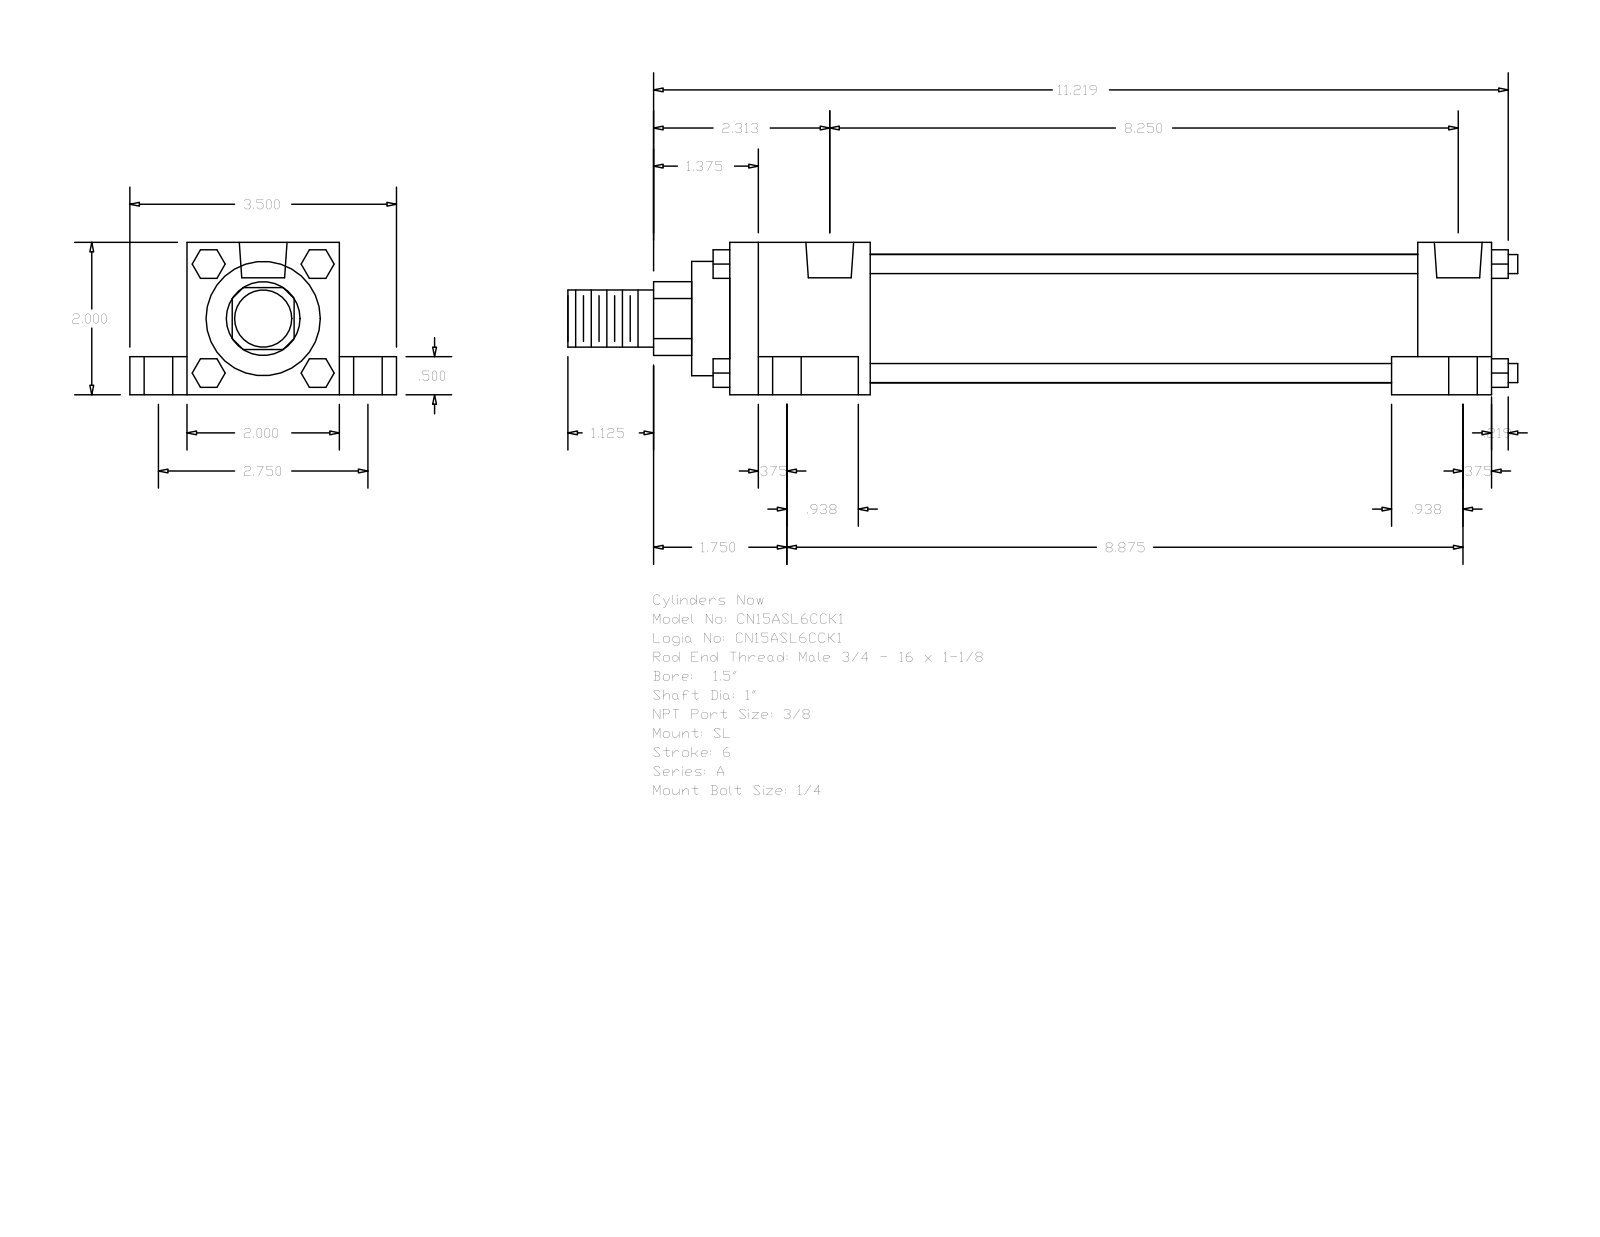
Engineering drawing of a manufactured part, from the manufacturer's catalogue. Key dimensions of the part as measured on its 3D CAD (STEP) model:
Part name (STEP PRODUCT): A_SL__0150_1
STEP written by: GSSL Pune (CONFIG_CONTROL_DESIGN)
Units: millimetres
Bodies: 0 solids, 148 faces (112 planar, 36 cylindrical, 0 other)
Overall size (bounding box): 316.71 × 88.9 × 50.8
Round holes (diameter × count): ⌀5.56 ×4, ⌀9.53 ×4, ⌀15.88 ×4, ⌀15.93 ×2
Round bosses / shafts (diameter × count): ⌀6.35 ×4, ⌀42.93 ×1, ⌀38.1 ×1, ⌀25.4 ×1, ⌀19.05 ×1
Partial cylindrical surfaces — rounded edges, fillets, slot ends (radius × count): R12.29 ×1
Main face-to-face distances: 50.8, 12.7, 38.1, 19.05, 69.85, 9.52, 254, 33.34, 229.39, 24.61
Hole centre spacings: 3.97, 34.96, 35.36, 37.73, 39.41, 69.84, 201.61, 205.58
